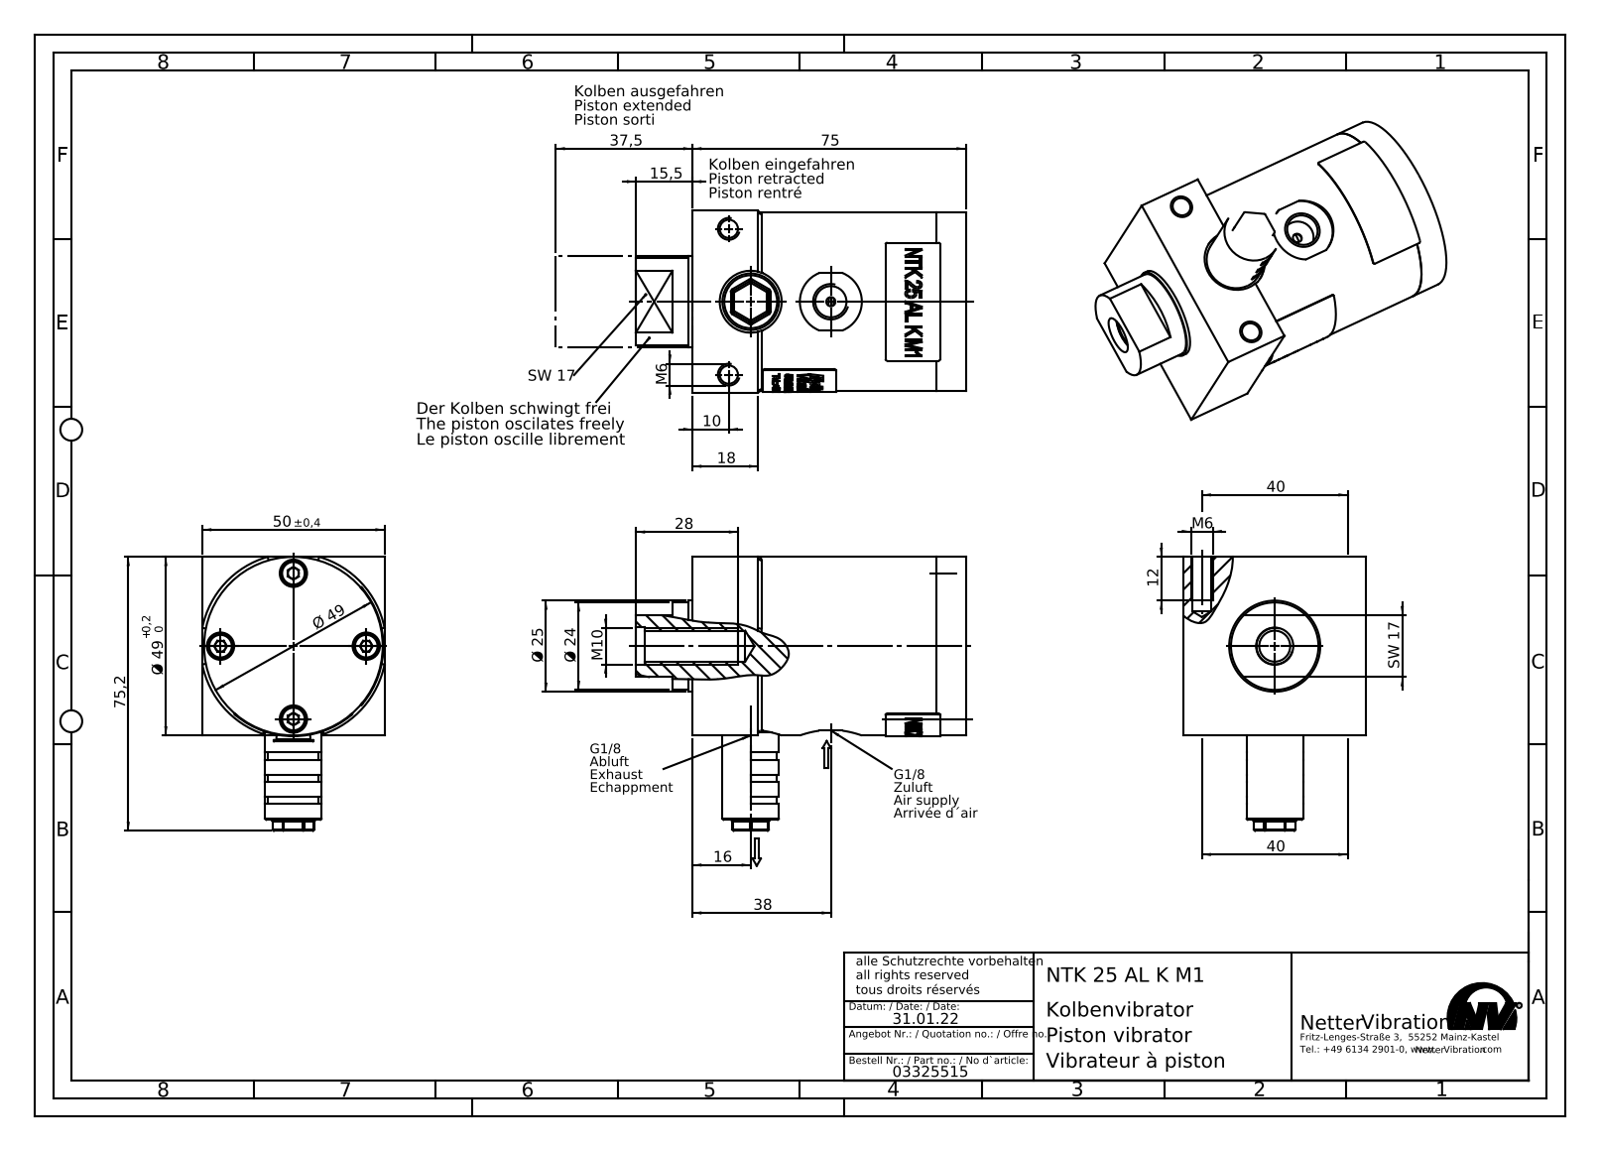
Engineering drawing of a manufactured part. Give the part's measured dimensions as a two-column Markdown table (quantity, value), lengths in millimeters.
| quantity | value |
| --- | --- |
| part name | NTK 25 AL K M1 #03325515 |
| STEP written by | SolidWorks 2015 (AUTOMOTIVE_DESIGN) |
| units | millimeters |
| bodies | 9 solids, 313 faces (112 planar, 116 cylindrical, 85 other) |
| overall size | 90.5 × 75 × 50 |
| volume | 135 172 mm³ |
| surface area | 36 348 mm² |
| round holes (diameter × count) | 3.3 × 4, 4.2 × 4, 7.5 × 4, 5 × 2, 8.57 × 2, 17 × 2, 8.5 × 1, 10.2 × 1, 25 × 1 |
| round bosses / shafts (diameter × count) | 7 × 4, 4 × 4, 49 × 1, 24 × 1, 15.5 × 1, 9.73 × 1 |
| partial cylindrical surfaces (radius × count) | 0.5 × 22, 7 × 1, 24.7 × 1 |
| main face-to-face distances | 67, 75, 8, 49, 47.5, 50, 1.5, 33.5, 19.5, 55.5 |
| hole center spacings | 20, 28.28, 40, 20.88, 34.41, 22 |
